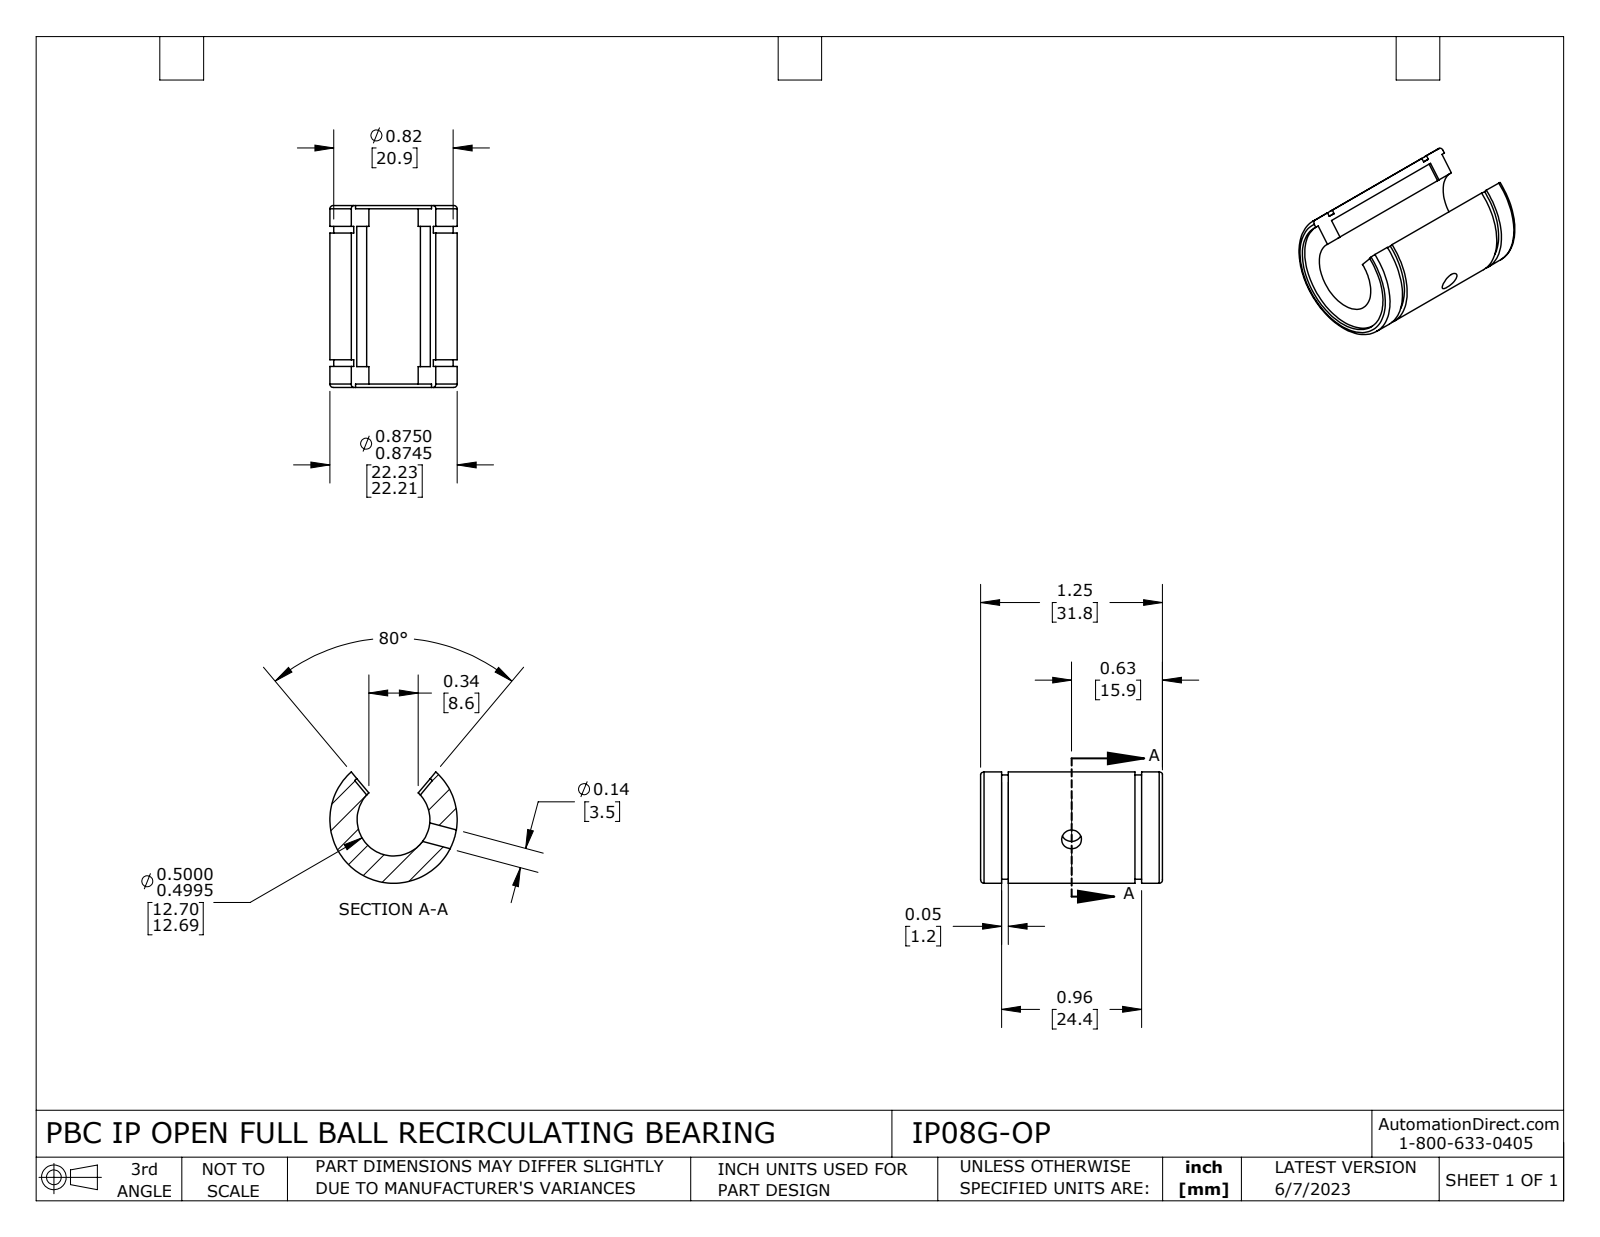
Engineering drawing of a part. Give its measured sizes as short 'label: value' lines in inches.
name: IP08G-OP
written by: SolidWorks 2021 (CONFIG_CONTROL_DESIGN)
unit: in
bodies: 1 solid, 40 faces (16 planar, 20 cylindrical, 4 other)
size: 1.25 × 0.875 × 0.765
volume: 0.365 in³; area: 5.471 in²
holes: 1× ⌀0.136
rounds: 1× R0.25, 1× R0.378, 1× R0.392, 1× R0.41, 1× R0.438
face distances: 1.204, 0.02, 0.121, 1.083, 0.167, 1.037, 0.917, 0.046, 0.023, 0.144
